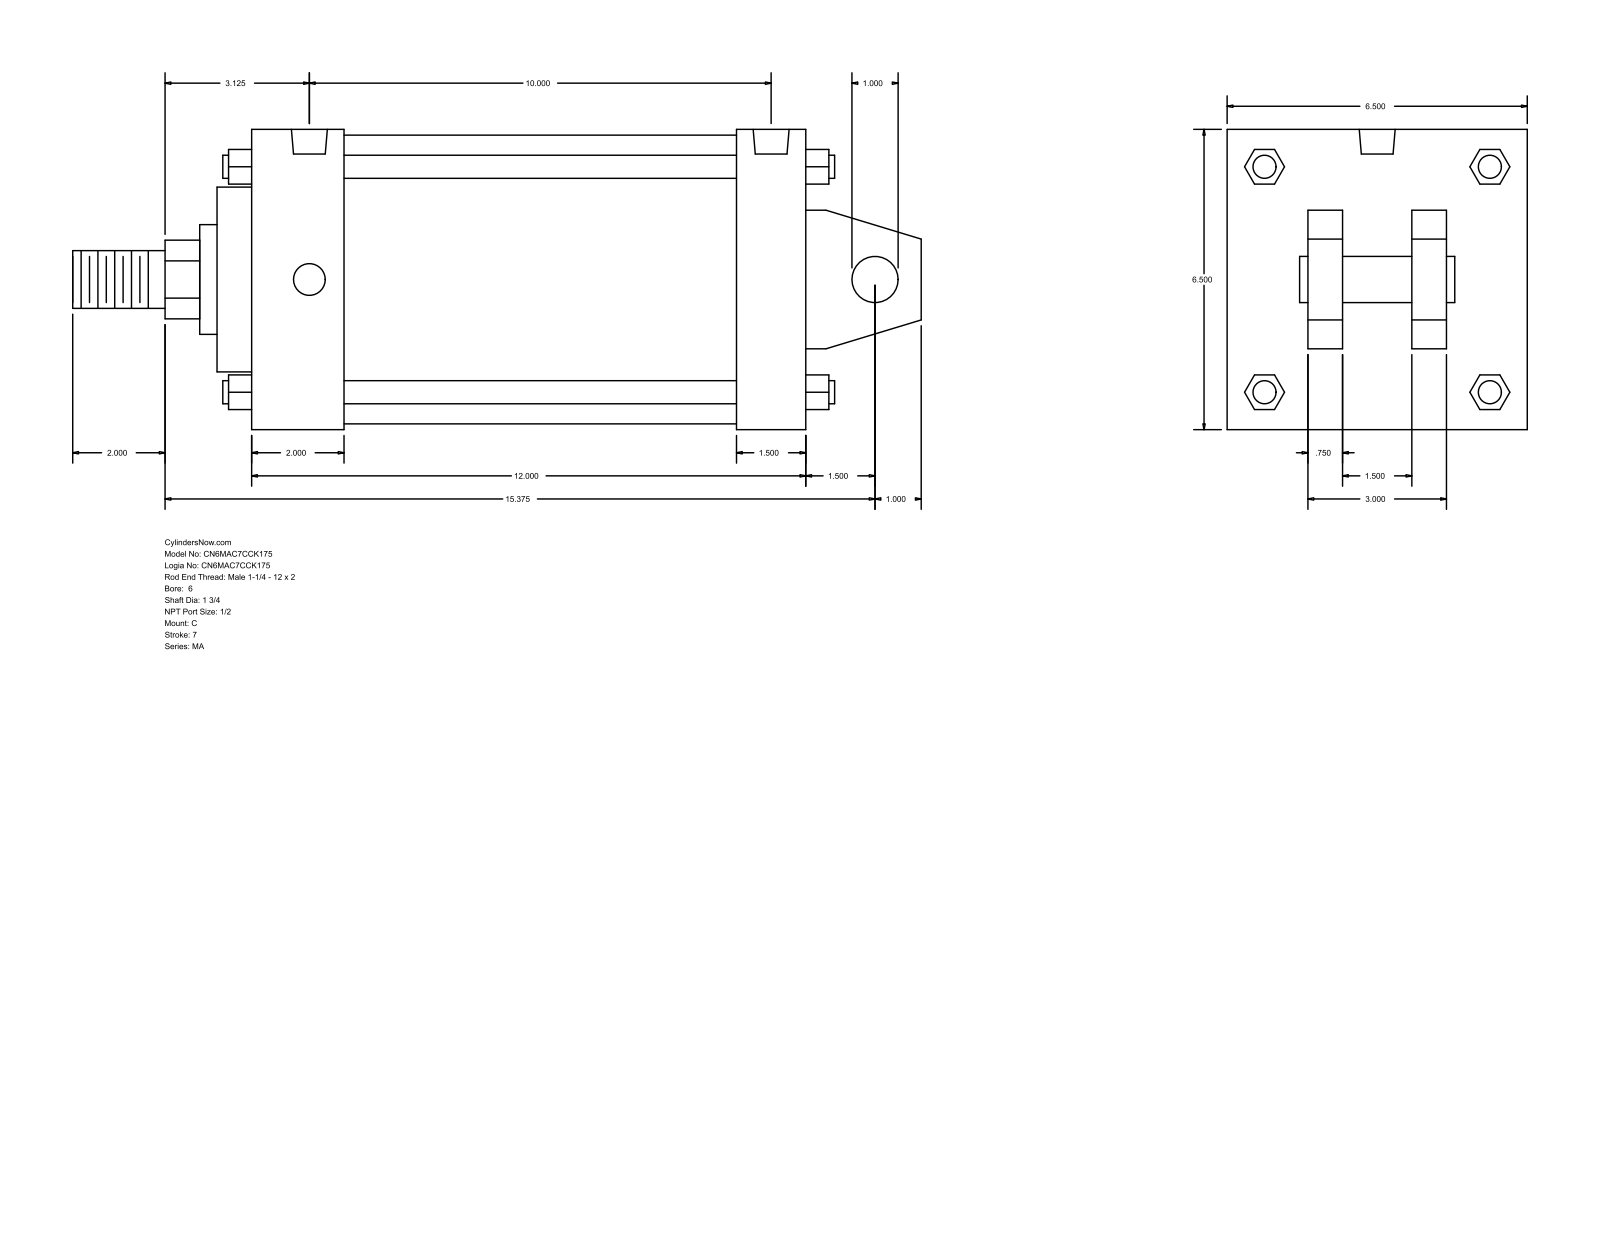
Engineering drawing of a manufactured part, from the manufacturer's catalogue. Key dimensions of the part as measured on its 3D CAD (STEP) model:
Part name (STEP PRODUCT): MA_C__0600_1.75
STEP written by: GSSL Pune (CONFIG_CONTROL_DESIGN)
Units: millimetres
Bodies: 0 solids, 141 faces (109 planar, 32 cylindrical, 0 other)
Overall size (bounding box): 466.73 × 165.1 × 165.1
Round holes (diameter × count): ⌀17.46 ×4, ⌀19.77 ×2
Round bosses / shafts (diameter × count): ⌀12.7 ×4, ⌀158.75 ×1, ⌀101.6 ×1, ⌀60.33 ×1, ⌀44.45 ×1, ⌀31.75 ×1, ⌀25.4 ×1
Partial cylindrical surfaces — rounded edges, fillets, slot ends (radius × count): R21.63 ×1
Main face-to-face distances: 165.1, 304.81, 19.05, 63.5, 101.6, 50.8, 44.45, 120.65, 266.7, 57.15
Hole centre spacings: 254
